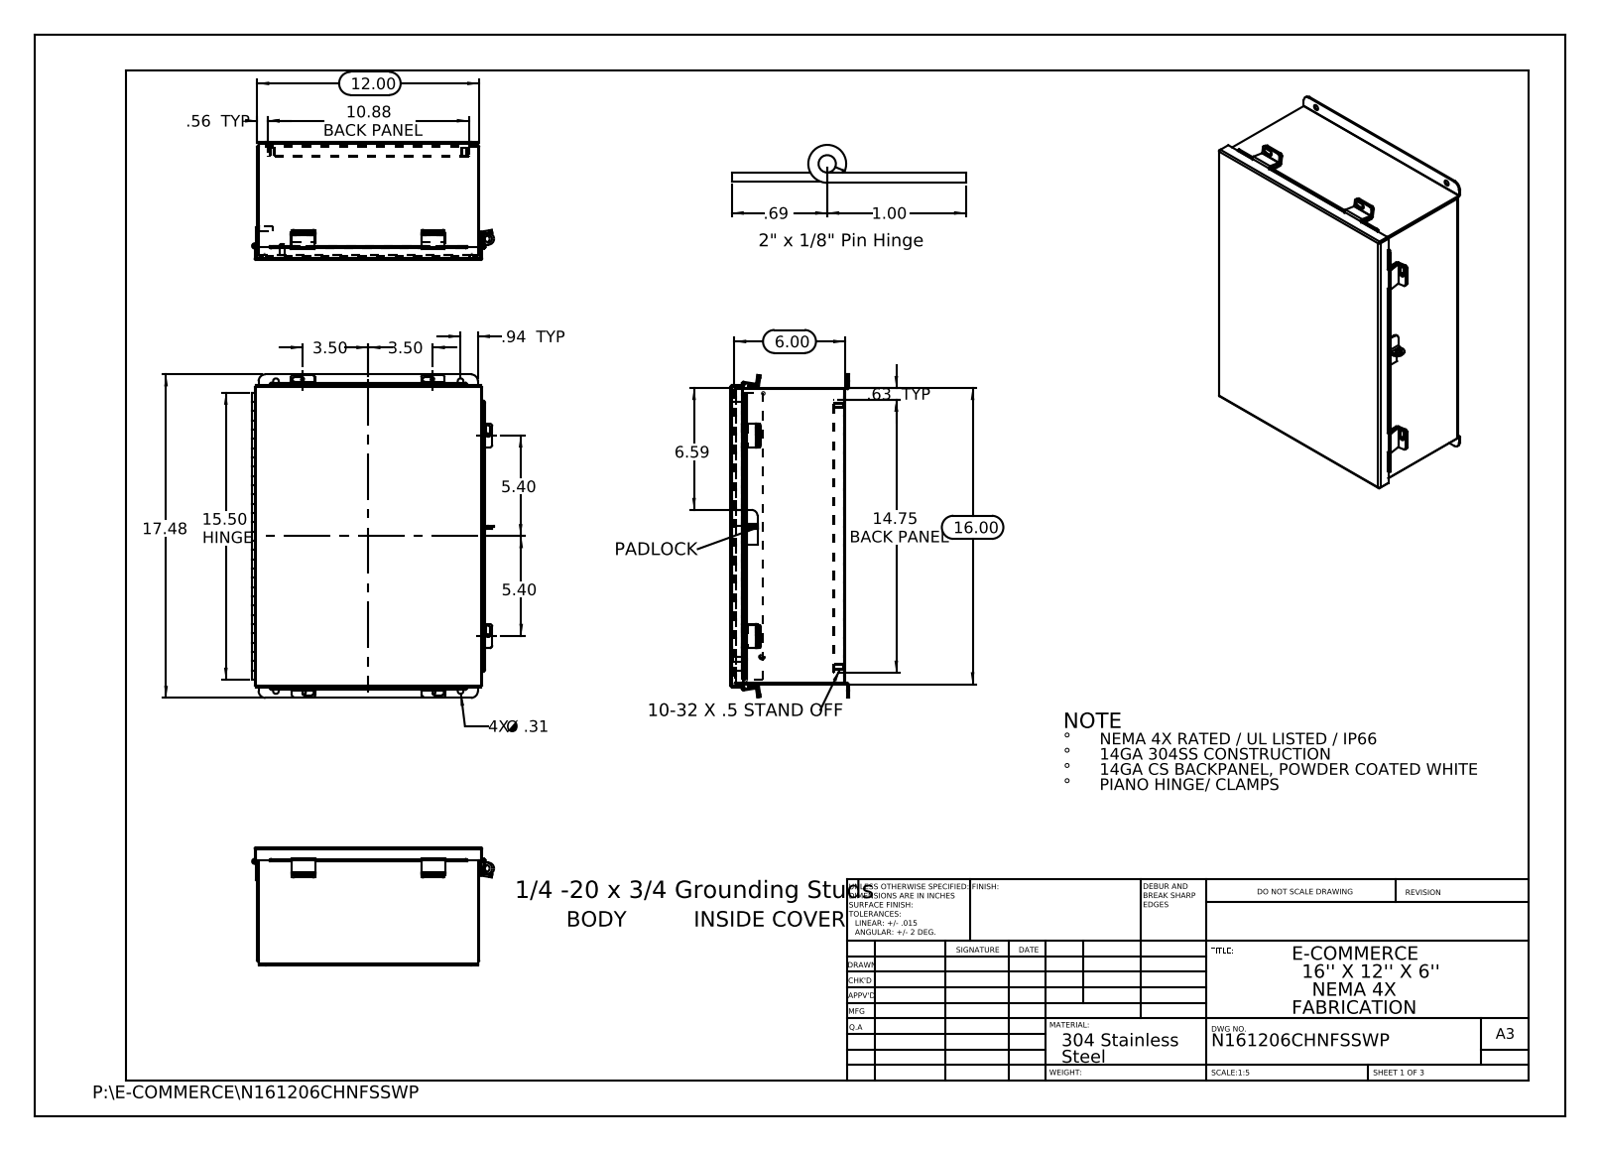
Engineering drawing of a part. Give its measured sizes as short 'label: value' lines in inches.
name: N161206CHNFSSWP JIC Cover Clamp; N161206CHNFSSWP Hinge Body Side; N161206CHNFSSWP JIC Enclosure Template; N161206CHNFSSWP JIC_Standoff (+8 more)
written by: SolidWorks 2013 (CONFIG_CONTROL_DESIGN)
unit: in
bodies: 27 solids, 866 faces (539 planar, 307 cylindrical, 20 other)
size: 17.476 × 13.072 × 6.39
volume: 75.45 in³; area: 2 054 in²
holes: 10× ⌀0.25, 4× ⌀0.187, 4× ⌀0.312, 1× ⌀0.125, 1× ⌀0.125, 1× ⌀0.373, 1× ⌀0.375
bosses: 4× ⌀0.313, 2× ⌀0.315, 2× ⌀0.236, 1× ⌀0.273, 1× ⌀0.25
rounds: 22× R0.125, 13× R0.013, 12× R0.009, 12× R0.088, 12× R0.133, 6× R0.083, 6× R0.1, 4× R0.375
face distances: 0.075, 6.128, 6.053, 6.203, 11.925, 0.074, 5.628, 0.575, 0.5, 5.553
hole spacings: 1.315, 10.258, 15.427, 18.48, 7, 9.976, 10.375, 14.126
